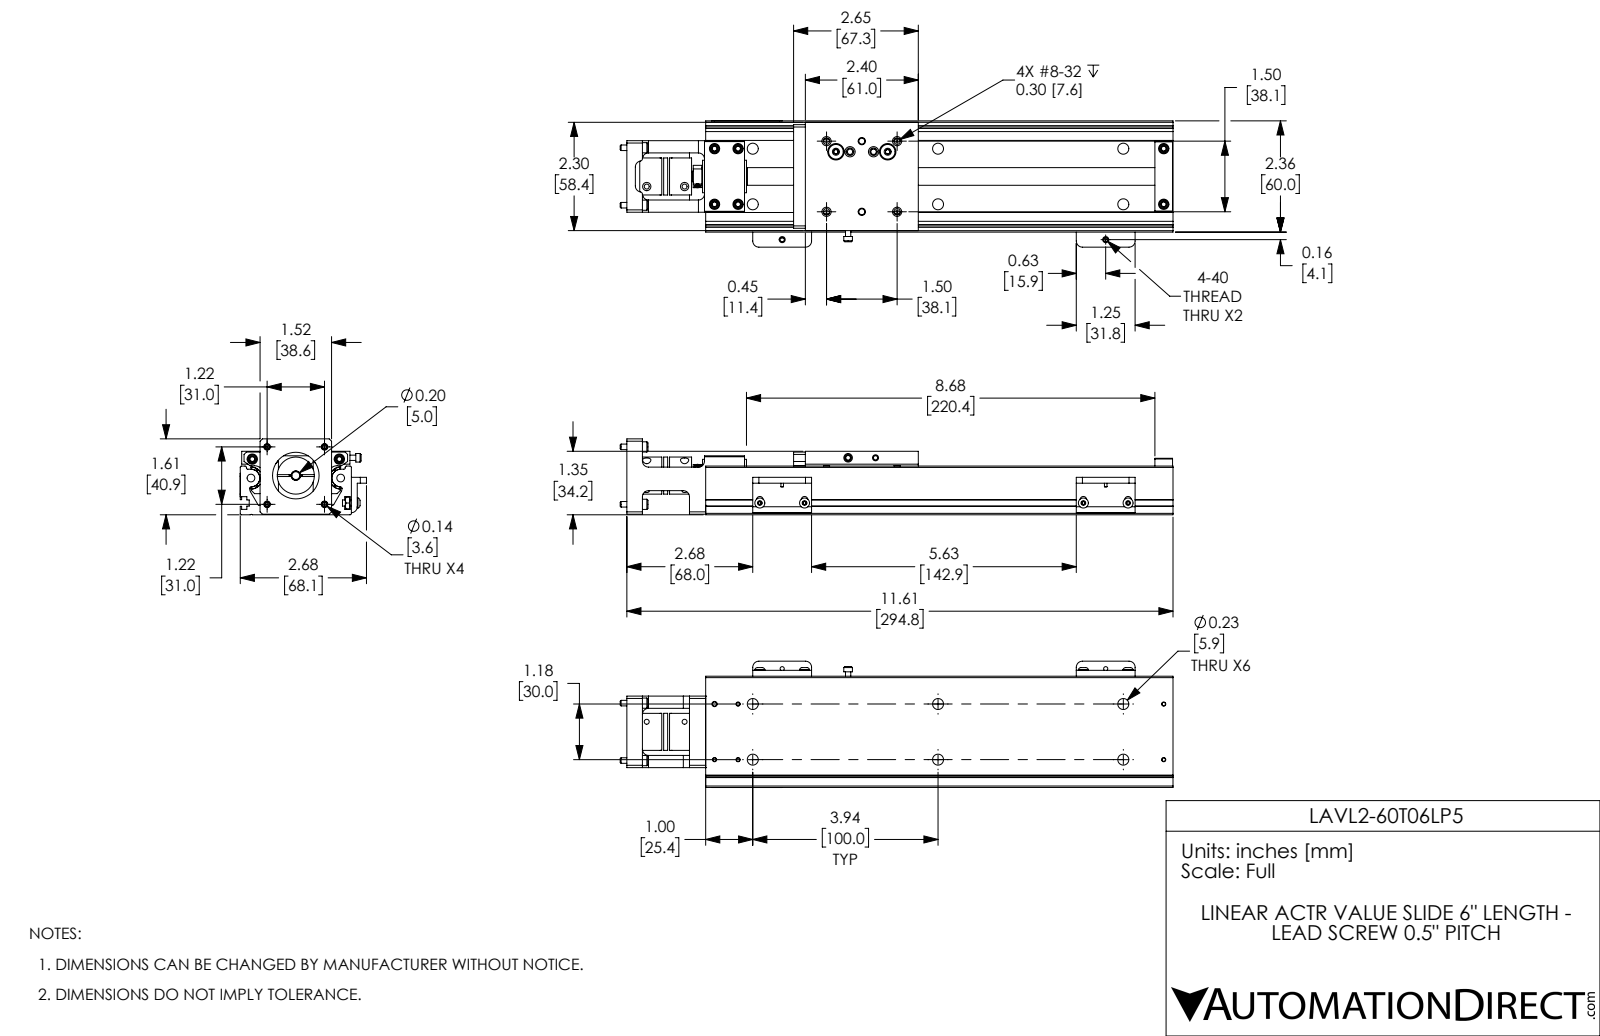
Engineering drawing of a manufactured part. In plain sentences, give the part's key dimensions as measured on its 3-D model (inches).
The part is named "LAVL2-60T06LP5; LAVL2-60T06LP5_BLOCK; LAVL2-60T06LP5_BODY". Its 3-D file was written by "SolidWorks 2017 (AUTOMOTIVE_DESIGN)". It is 52 solids with 2124 faces: 1295 planar, 521 cylindrical and 308 other. Overall it measures 11.748 by 2.683 by 1.612 inches. Its volume is 16.29 cubic inches and its surface area 224.1 square inches. Round holes: 18 of diameter 0.089, 10 of diameter 0.141, 10 of diameter 0.219, 6 of diameter 0.136, 6 of diameter 0.234, 4 of diameter 0.141, 2 of diameter 0.03, 2 of diameter 0.1, 2 of diameter 0.106, 2 of diameter 0.125, 2 of diameter 0.159, 2 of diameter 0.165. Round bosses or shafts: 15 of diameter 0.112, 11 of diameter 0.183, 4 of diameter 0.217, 4 of diameter 0.213, 4 of diameter 0.118, 2 of diameter 0.312, 2 of diameter 0.19, 2 of diameter 0.164. Partial cylindrical surfaces (rounded edges, fillets, slot ends): 20 of radius 0.13, 12 of radius 0.03, 8 of radius 0.07, 4 of radius 0.06, 3 of radius 0.02, 2 of radius 0.04, 2 of radius 0.05, 2 of radius 0.065. The main face-to-face distances are 0.2, 2.362, 1.348, 1.148, 0.421, 1.941, 0.14, 0.115, 0.185, 0.281. The hole center spacings are 1.181, 1.5, 0.75, 0.858, 0.863, 1.677, 3.937, 4.11.
